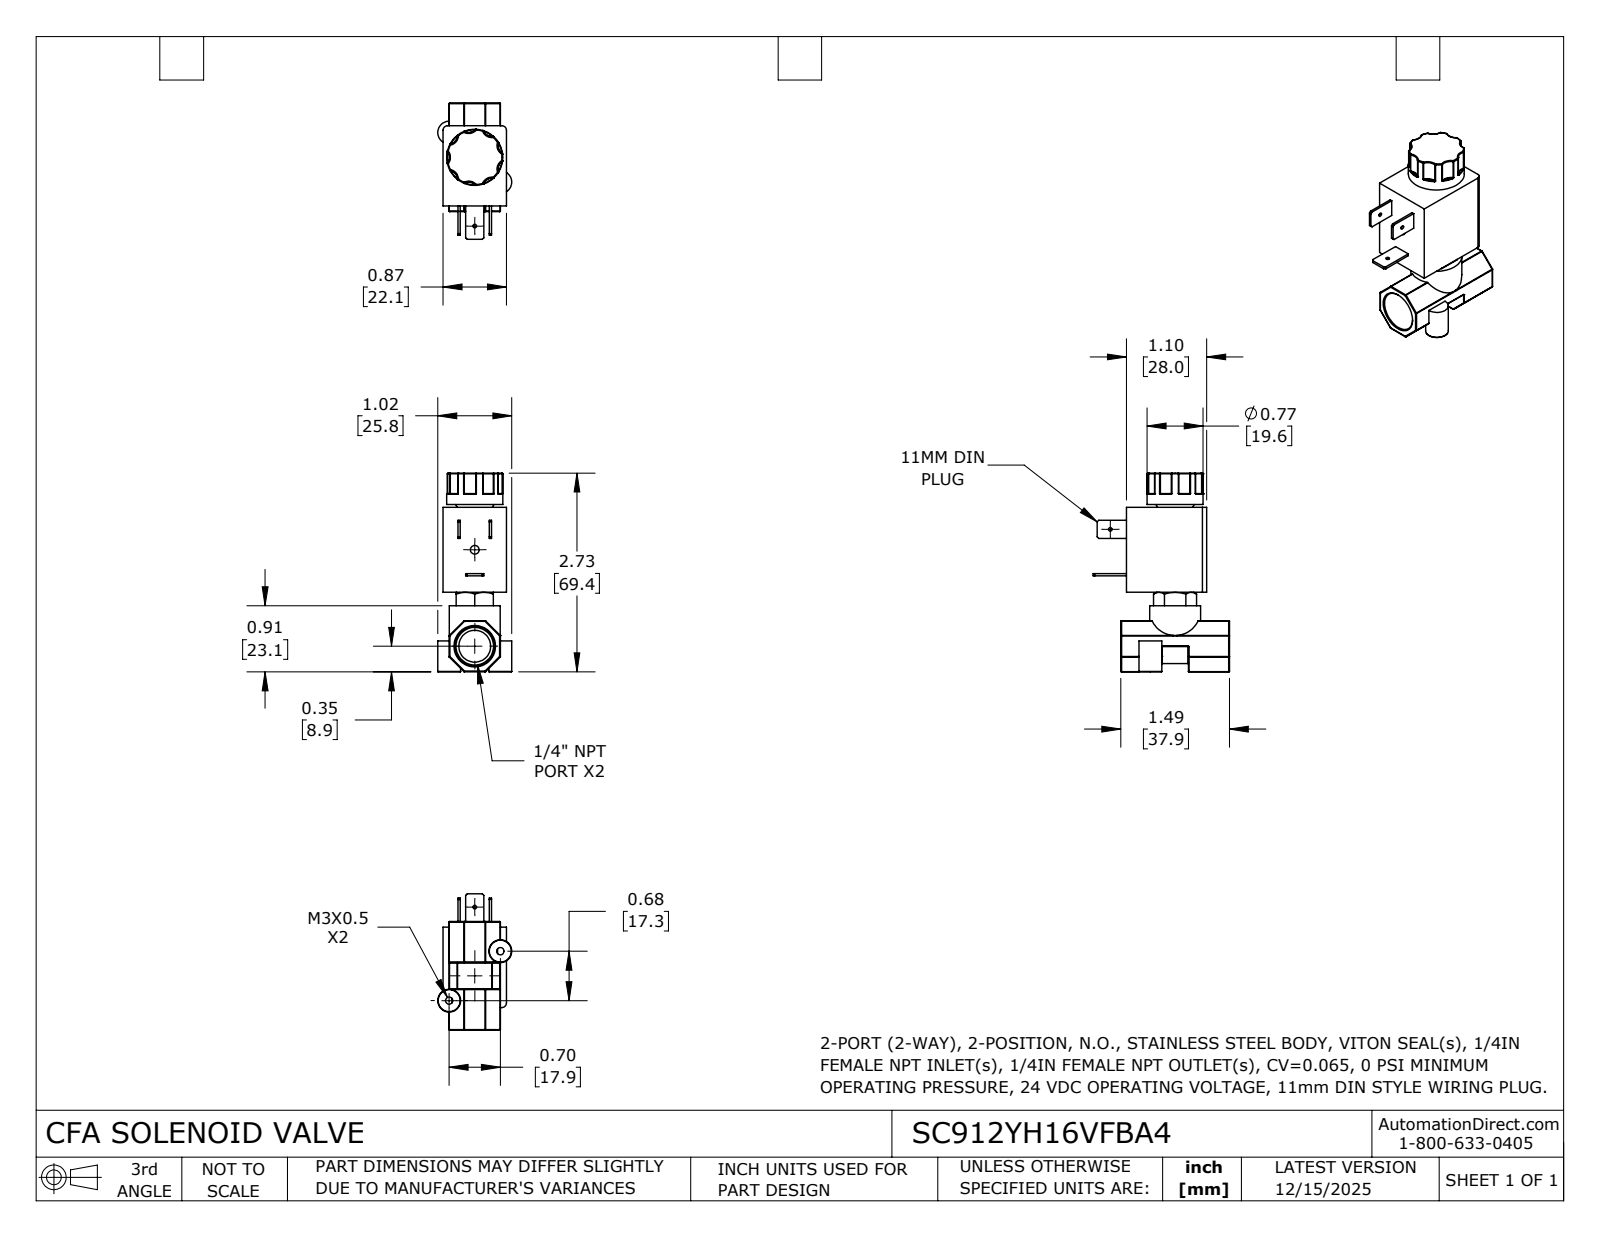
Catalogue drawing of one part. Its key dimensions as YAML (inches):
part_name: "SC912YH16VFBA4"
step_written_by: "SolidWorks 2024 (CONFIG_CONTROL_DESIGN)"
units: inches
bodies: {solids: 1, faces: 350, planar: 74, cylindrical: 107, other: 169}
overall_size: [2.731, 1.874, 1.017]
volume: 1.823
surface_area: 16.29
round_holes:
  - {diameter: 0.05, count: 2}
  - {diameter: 0.1, count: 2}
  - {diameter: 0.12, count: 1}
  - {diameter: 0.438, count: 1}
round_bosses_or_shafts:
  - {diameter: 0.313, count: 2}
  - {diameter: 0.77, count: 1}
  - {diameter: 0.7, count: 1}
partial_cylinders:
  - {radius: 0.01, count: 42}
  - {radius: 0.005, count: 14}
  - {radius: 0.133, count: 7}
  - {radius: 0.06, count: 2}
  - {radius: 0.132, count: 2}
  - {radius: 0.237, count: 1}
  - {radius: 0.314, count: 1}
face_to_face_distances: [0.87, 0.704, 1.104, 1.167, 0.083, 0.787, 1.094, 2.261, 2.731, 1.637]
hole_center_spacings: [0.7, 0.979, 1.326, 1.333]
